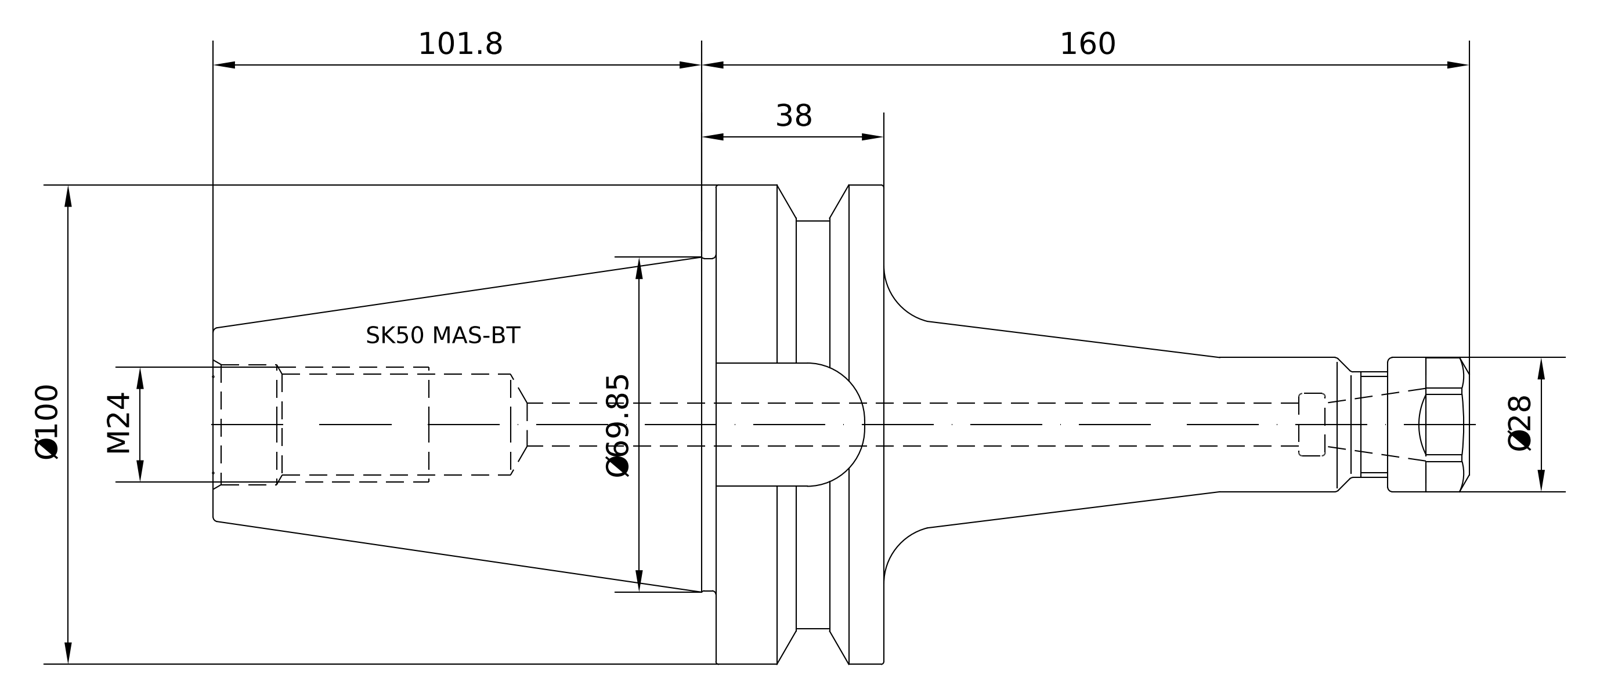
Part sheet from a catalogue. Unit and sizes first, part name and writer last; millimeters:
Units: millimetres
Overall size (bounding box): 261.8 × 99.97 × 99.97
Round holes (diameter × count): ⌀10.5 ×1, ⌀20.75 ×1, ⌀25.02 ×1, ⌀25.7 ×1
Round bosses / shafts (diameter × count): ⌀99.97 ×1, ⌀84.75 ×1, ⌀69.15 ×1, ⌀28 ×1, ⌀24.01 ×1, ⌀22 ×1
Partial cylindrical surfaces — rounded edges, fillets, slot ends (radius × count): R12.9 ×1
Main face-to-face distances: 35, 70.4, 139.2, 104.2, 104.8, 139.8, 244, 25, 25.8, 261.8
Volume: 566 559 mm³ · Surface area: 64 859 mm²
Bodies: 2 solids, 130 faces (34 planar, 26 cylindrical, 70 other)
Part name (STEP PRODUCT): 50-522-16; 83-912-16; 50-522-16_ASM
STEP written by: PRO/ENGINEER BY PARAMETRIC TECHNOLOGY CORPORATION, 2010430 (CONFIG_CONTROL_DESIGN)
